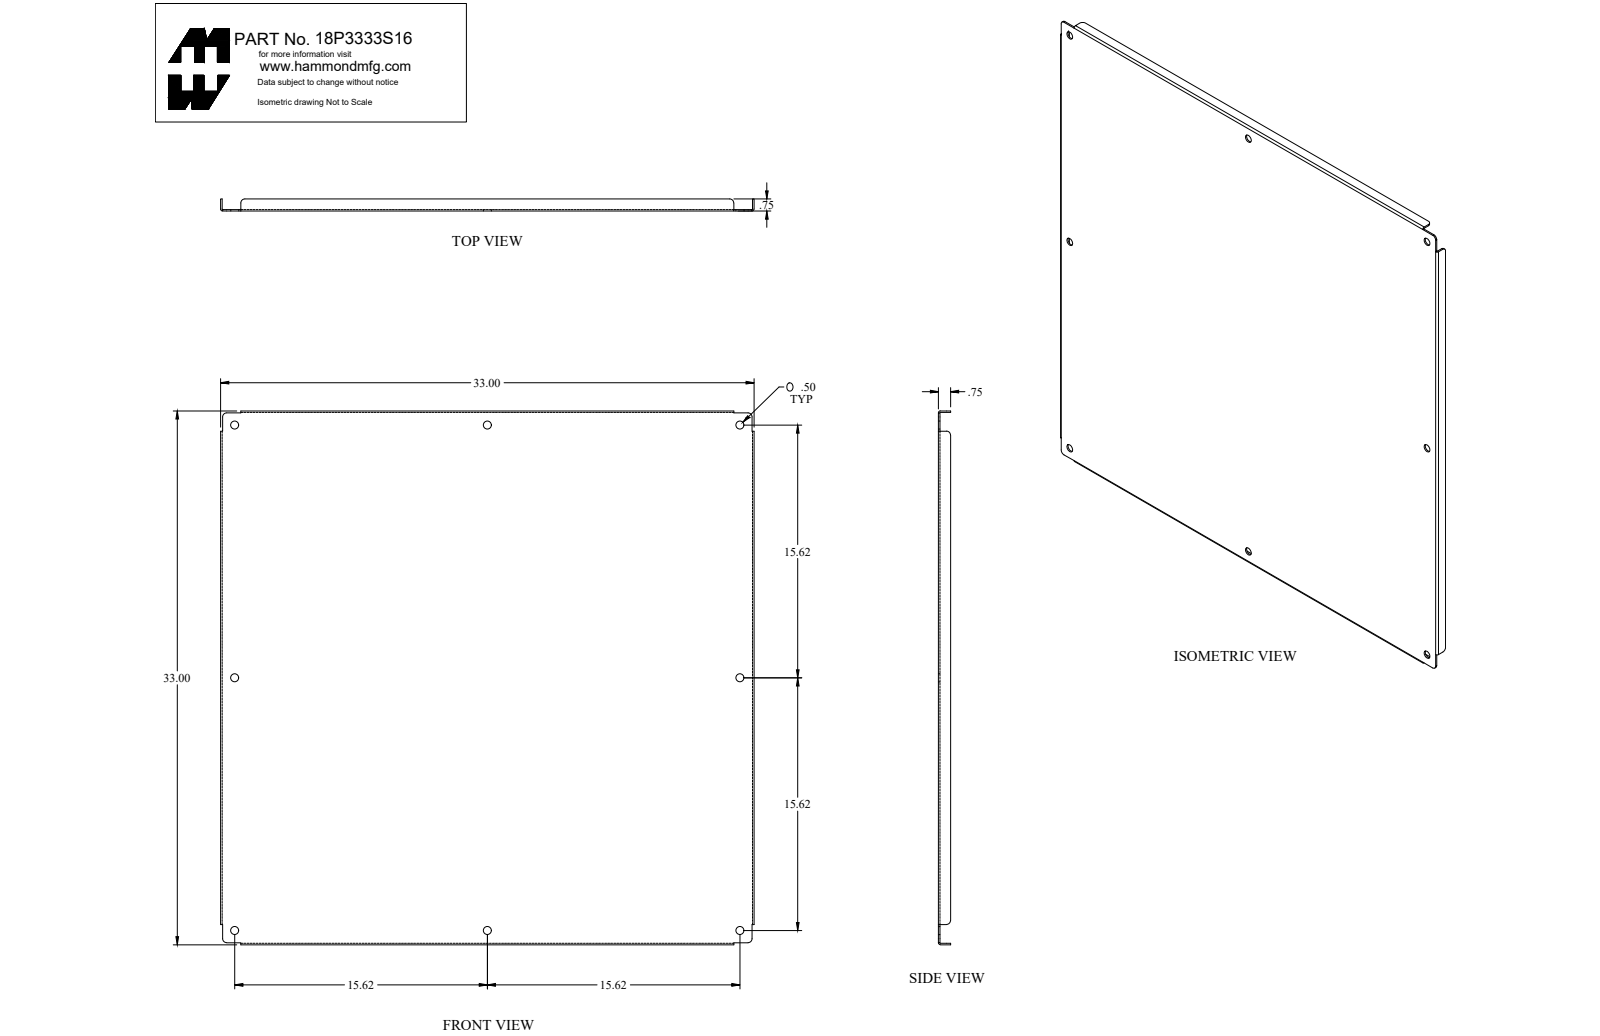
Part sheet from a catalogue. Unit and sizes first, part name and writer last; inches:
Units: inches
Overall size (bounding box): 33 × 33 × 0.75
Round holes (diameter × count): ⌀0.5 ×8
Partial cylindrical surfaces — rounded edges, fillets, slot ends (radius × count): R0.25 ×8, R0.03 ×4, R0.125 ×4
Main face-to-face distances: 0.095, 32.905, 33, 32.81, 0.75, 0.655, 0.125, 32.875, 0.03, 32.78
Hole centre spacings: 15.625, 34.939, 31.25, 22.097, 44.195
Volume: 110.4 in³ · Surface area: 2 338 in²
Bodies: 1 solid, 66 faces (30 planar, 36 cylindrical, 0 other)
Part name (STEP PRODUCT): 18P3333S16_Default
STEP written by: SolidWorks 2018 (CONFIG_CONTROL_DESIGN)
